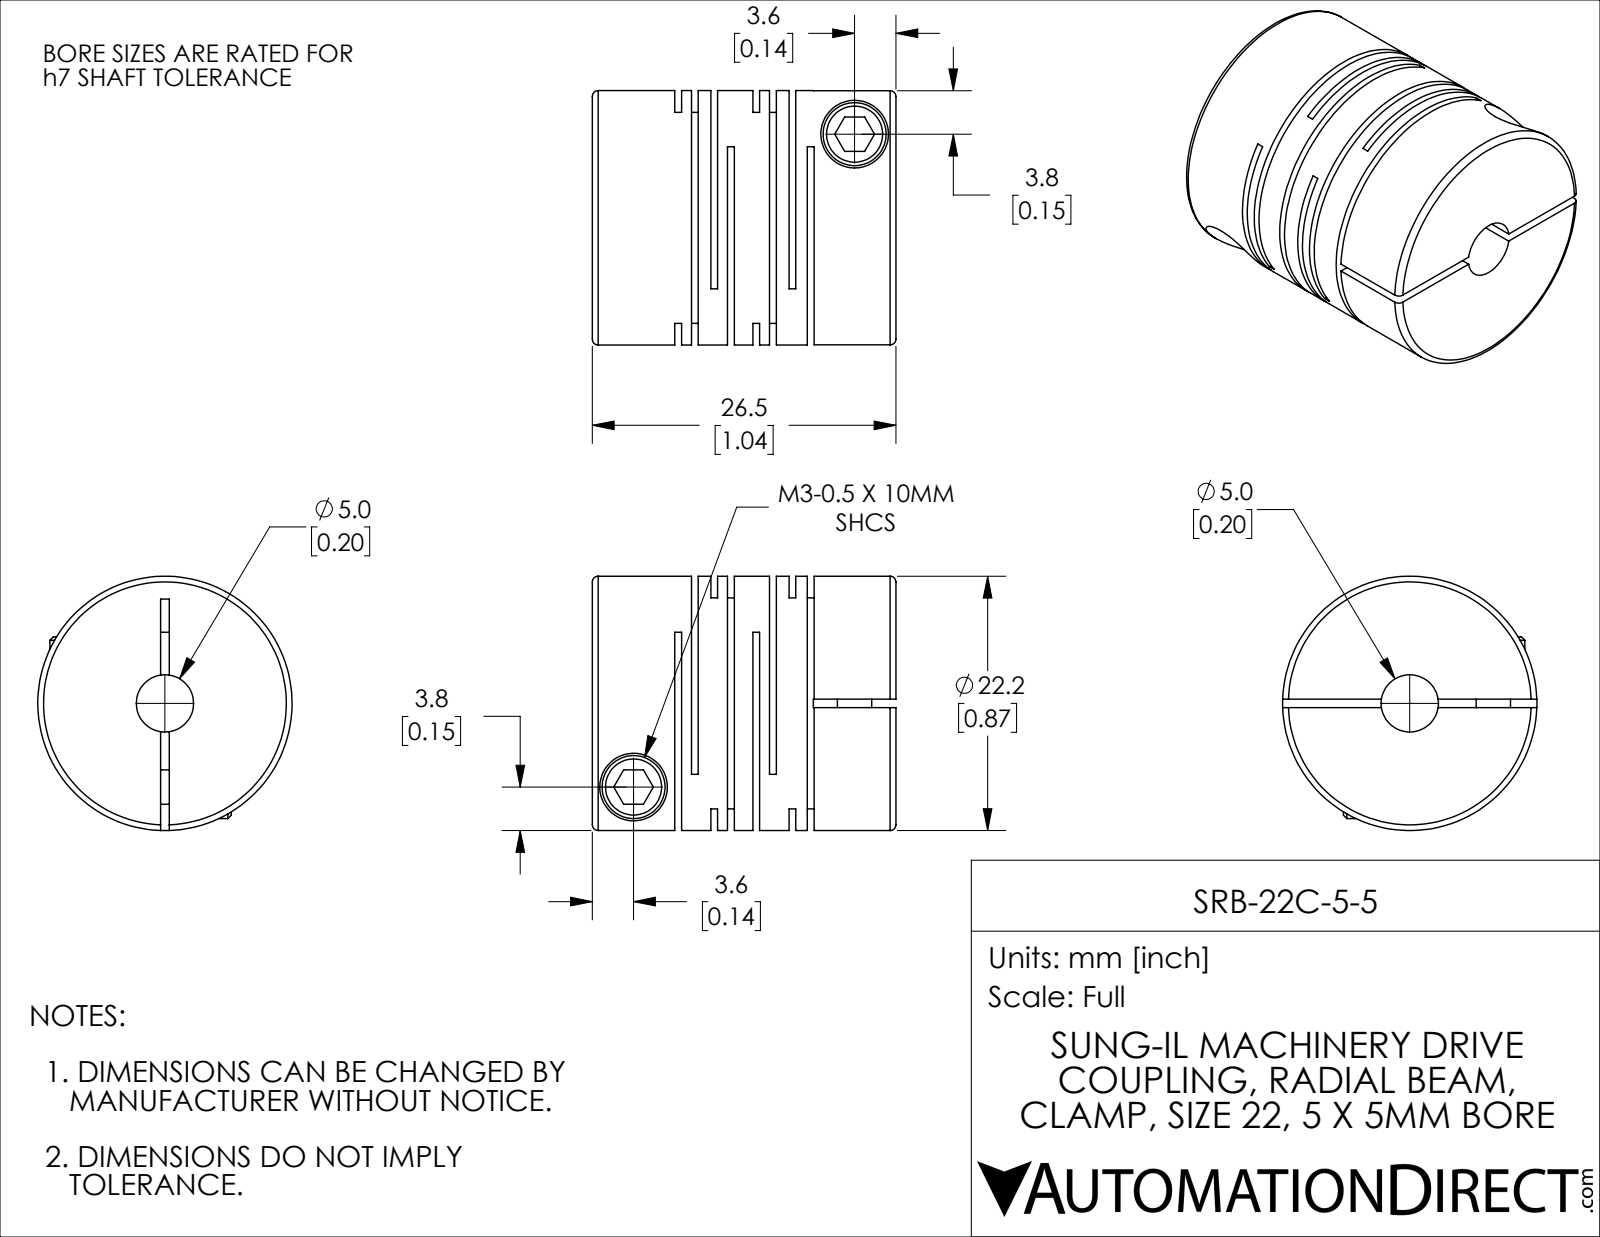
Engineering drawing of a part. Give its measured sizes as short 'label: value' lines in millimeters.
name: SRB-22C-5-5
written by: SolidWorks 2021 (CONFIG_CONTROL_DESIGN)
unit: mm
bodies: 1 solid, 115 faces (60 planar, 42 cylindrical, 13 other)
size: 26.5 × 22.2 × 22.2
volume: 7 945 mm³; area: 8 283 mm²
holes: 2× ⌀3, 2× ⌀5.9, 1× ⌀5
bosses: 2× ⌀5.5, 1× ⌀22.2
face distances: 0.59, 3.15, 6.82, 1.45, 5.37, 1.7, 3.67, 6.23, 0.86, 2.56
